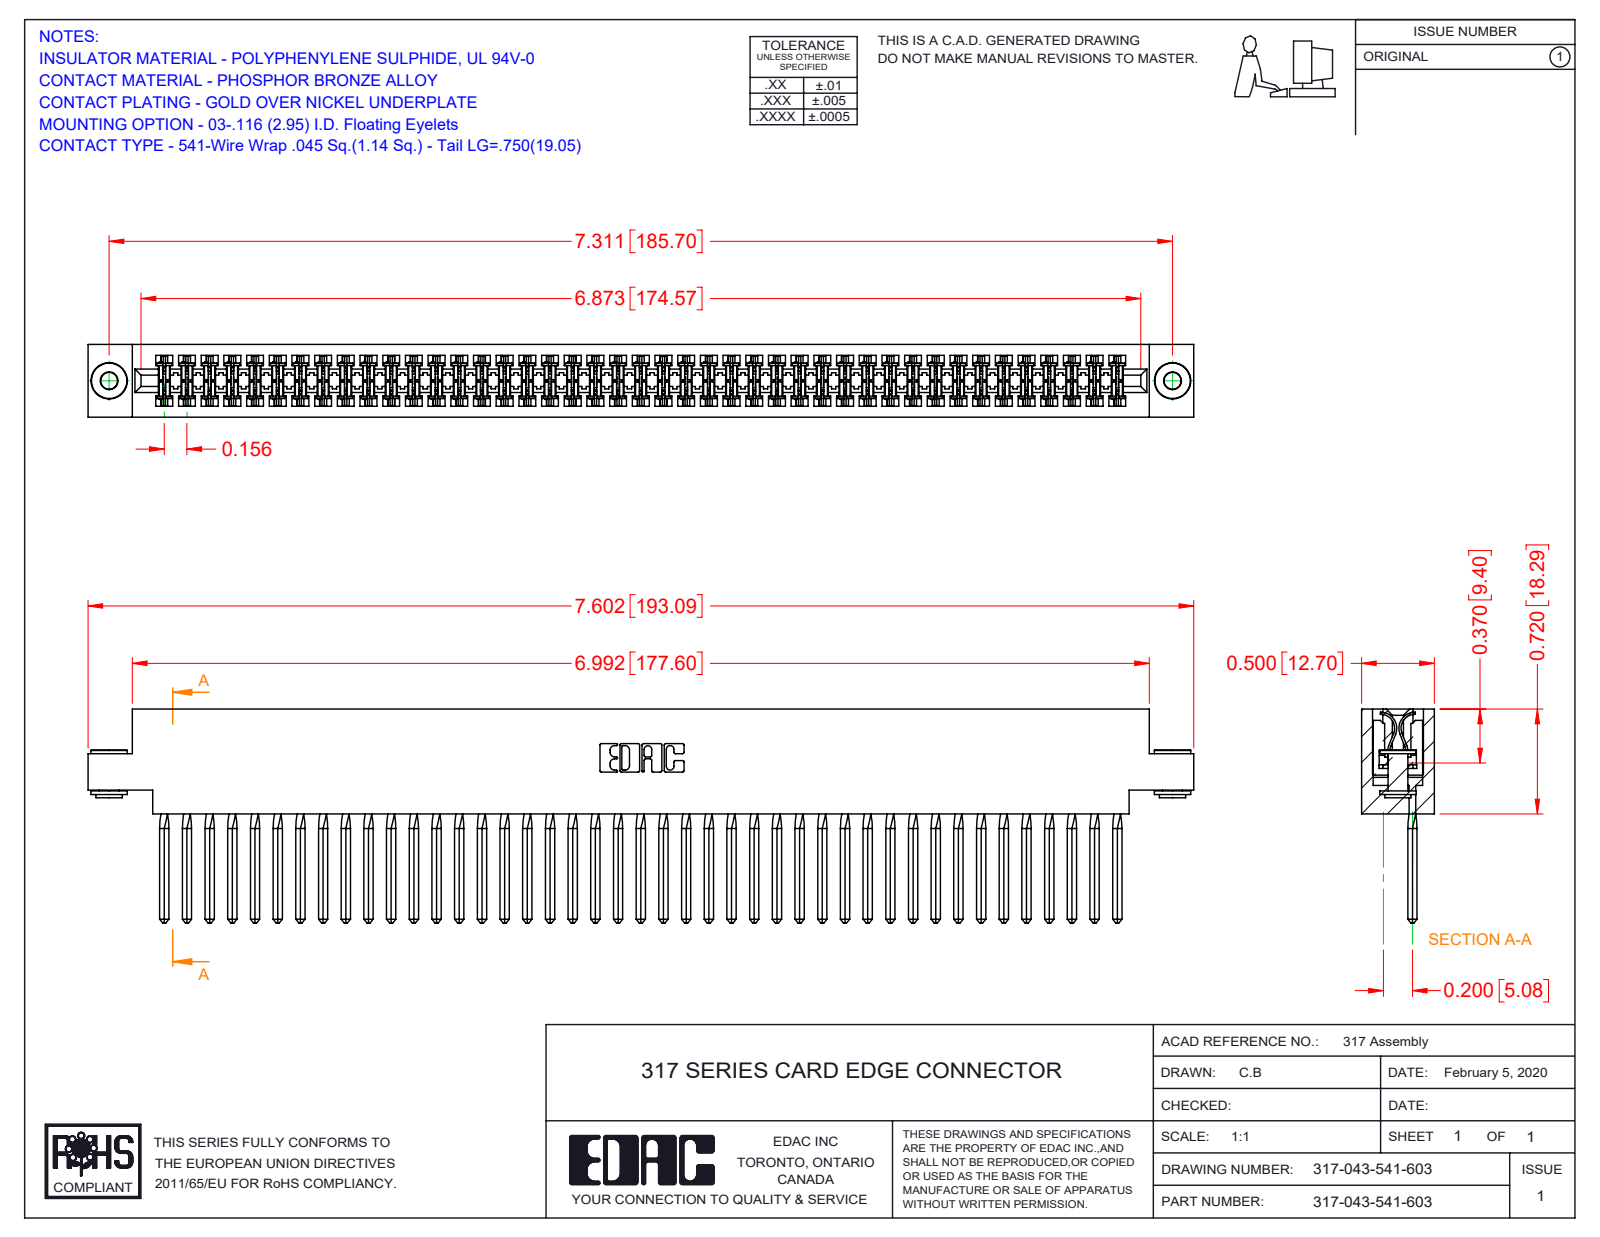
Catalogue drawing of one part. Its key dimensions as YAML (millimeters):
part_name: "317-290-002_541; 317-043-541-603; 317 Part_.156 Dia - TH; 345-250-002_345-250-002-102"
step_written_by: "SolidWorks 2016 (CONFIG_CONTROL_DESIGN)"
units: millimeters
bodies: {solids: 46, faces: 6676, planar: 5400, cylindrical: 1096, other: 180}
overall_size: [193.1, 37.3, 12.7]
volume: 31360
surface_area: 44570
round_holes:
  - {diameter: 2.9, count: 2}
  - {diameter: 4, count: 2}
round_bosses_or_shafts:
  - {diameter: 6.4, count: 2}
  - {diameter: 4.6, count: 2}
  - {diameter: 3.5, count: 2}
partial_cylinders:
  - {radius: 0.4, count: 86}
  - {radius: 0.3, count: 22}
  - {radius: 0.2, count: 6}
  - {radius: 0.8, count: 6}
  - {radius: 0.7, count: 3}
  - {radius: 2.4, count: 2}
  - {radius: 2.5, count: 2}
  - {radius: 2.8, count: 2}
face_to_face_distances: [12.7, 1.9, 10.8, 8.9, 5, 2.8, 18.3, 2.9, 5.4, 7.3]
hole_center_spacings: [185.7]
